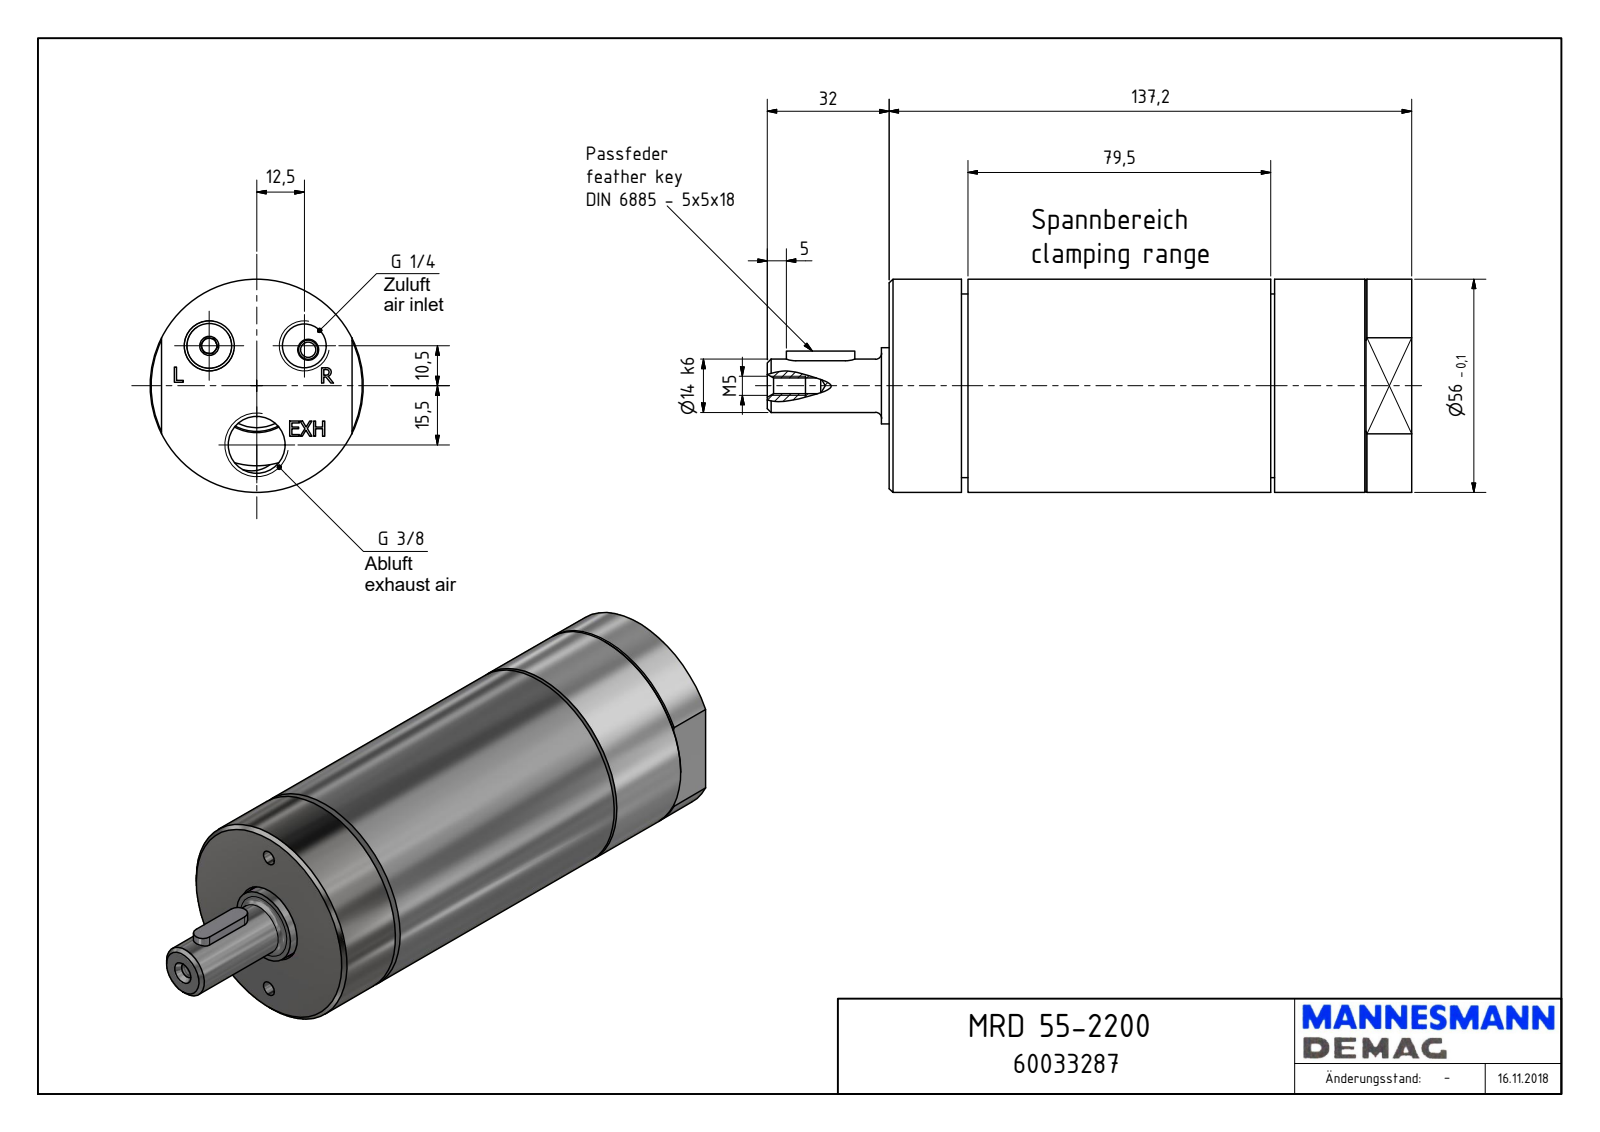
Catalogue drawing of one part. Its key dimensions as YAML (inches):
part_name: "MRD 55-2200_60033287"
step_written_by: "Autodesk Inventor 2018 (AUTOMOTIVE_DESIGN)"
units: inches
bodies: {solids: 1, faces: 153, planar: 98, cylindrical: 22, other: 33}
overall_size: [6.661, 2.205, 2.205]
volume: 20.55
surface_area: 55.23
round_holes:
  - {diameter: 0.157, count: 3}
  - {diameter: 0.163, count: 1}
  - {diameter: 0.451, count: 1}
  - {diameter: 0.589, count: 1}
  - {diameter: 0.827, count: 1}
  - {diameter: 0.837, count: 1}
  - {diameter: 1.024, count: 1}
  - {diameter: 1.905, count: 1}
round_bosses_or_shafts:
  - {diameter: 2.205, count: 1}
  - {diameter: 1.897, count: 1}
  - {diameter: 0.785, count: 1}
  - {diameter: 0.551, count: 1}
partial_cylinders:
  - {radius: 0.098, count: 2}
face_to_face_distances: [5.402, 0.815, 4.587, 3.945, 3.13, 1.457, 3.984, 0.748, 0.067, 3.197]
hole_center_spacings: [0.643, 0.827, 1.136, 1.334, 0.217, 0.61, 0.984, 1.437]
